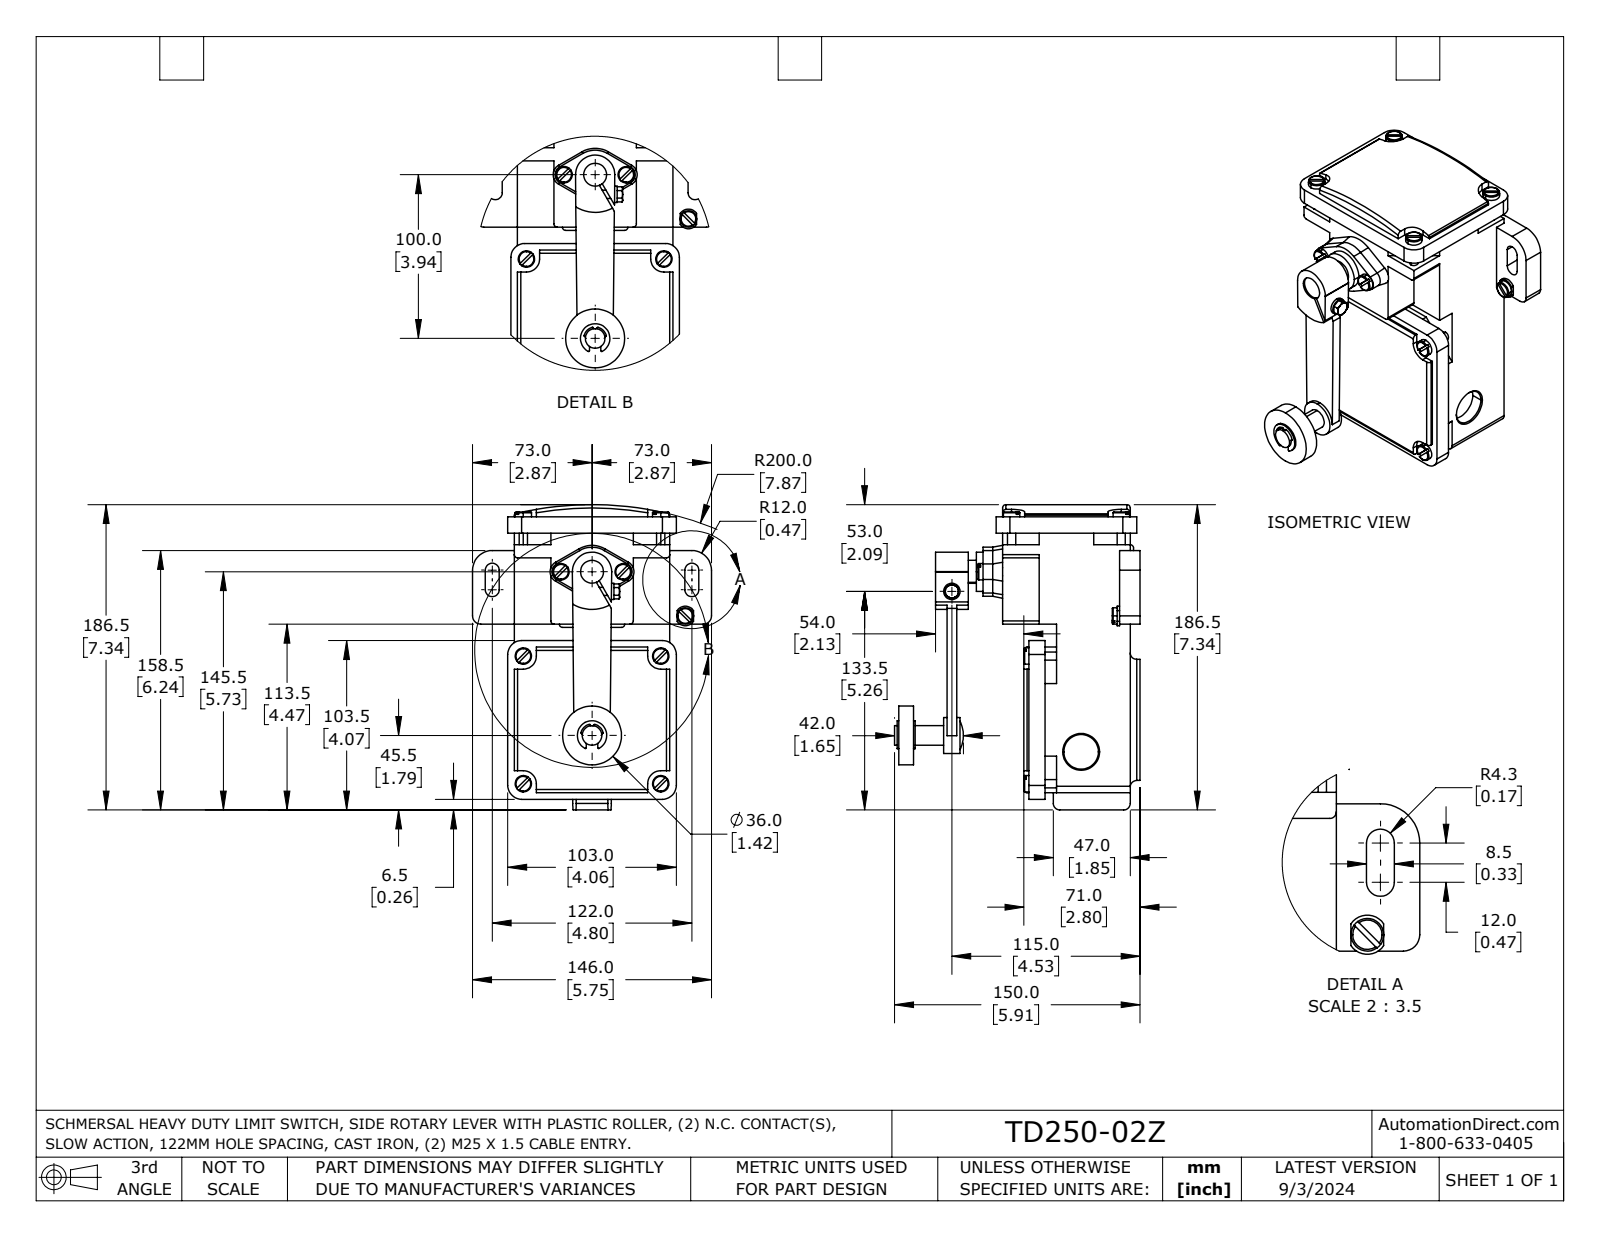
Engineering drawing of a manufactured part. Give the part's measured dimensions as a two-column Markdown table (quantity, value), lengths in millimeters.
| quantity | value |
| --- | --- |
| part name | TD 250-02Z |
| STEP written by | SolidWorks 2023 (AUTOMOTIVE_DESIGN) |
| units | millimeters |
| bodies | 1 solid, 421 faces (207 planar, 138 cylindrical, 76 other) |
| overall size | 186.5 × 150 × 146 |
| volume | 1 227 000 mm³ |
| surface area | 111 400 mm² |
| round holes (diameter × count) | 4.1 × 1, 5 × 1, 14 × 1, 21.2 × 1 |
| round bosses / shafts (diameter × count) | 10 × 12, 5 × 8, 74 × 1, 36 × 1, 24 × 1, 22 × 1, 18 × 1, 12 × 1 |
| partial cylindrical surfaces (radius × count) | 2 × 10, 8 × 8, 8.5 × 8, 0.5 × 6, 4 × 4, 4.2 × 4, 1 × 2, 5 × 2 |
| main face-to-face distances | 6, 65, 95, 71, 13, 4, 10, 7, 17, 20 |
| hole center spacings | 125.9 |
